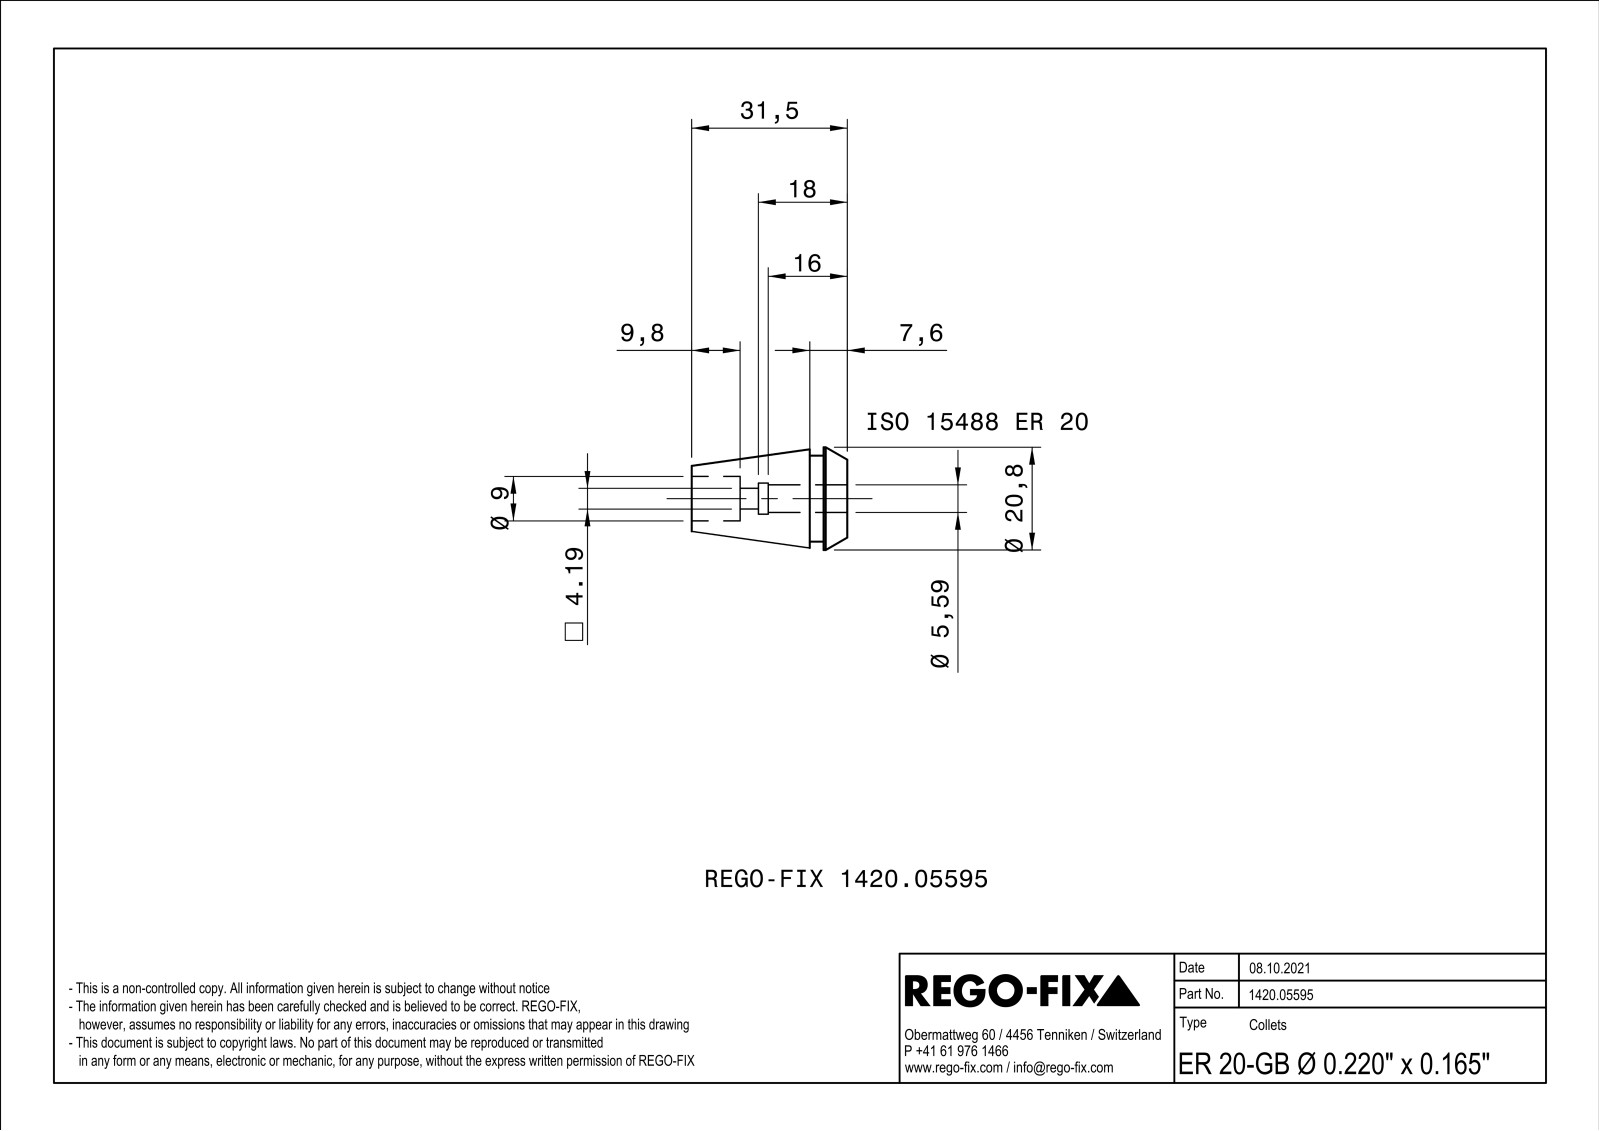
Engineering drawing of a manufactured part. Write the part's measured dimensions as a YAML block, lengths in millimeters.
part_name: "NOCUT"
step_written_by: "SIEMENS PLM Software Solid Edge ST10 (AUTOMOTIVE_DESIGN)"
units: millimeters
bodies: {solids: 1, faces: 152, planar: 60, cylindrical: 28, other: 64}
overall_size: [31.5, 20.79, 20.79]
volume: 5141
surface_area: 4729
round_holes:
  - {diameter: 5.59, count: 1}
  - {diameter: 9, count: 1}
round_bosses_or_shafts:
  - {diameter: 17.4, count: 1}
partial_cylinders:
  - {radius: 2.5, count: 1}
  - {radius: 3.15, count: 1}
face_to_face_distances: [0.8, 4.8, 31.5, 26.7, 7.6, 2.8, 23.9, 21.7, 16.9, 14.1]
